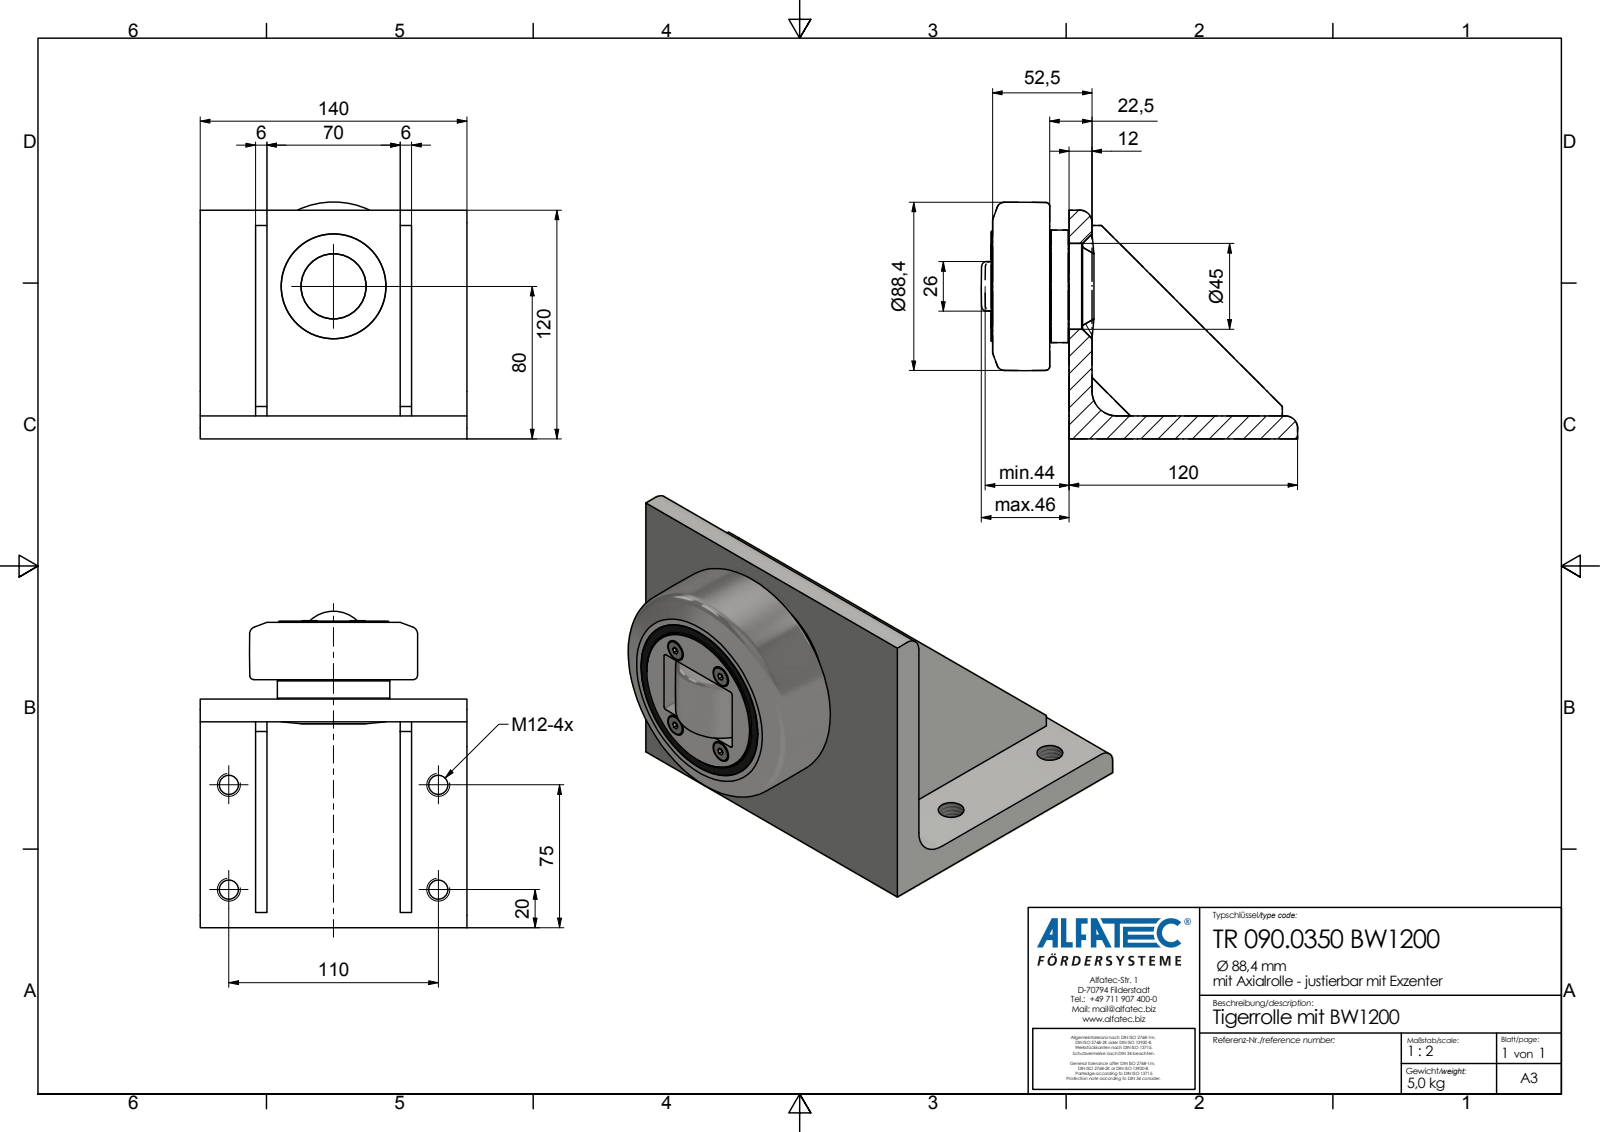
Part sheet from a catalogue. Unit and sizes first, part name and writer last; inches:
Units: inches
Overall size (bounding box): 6.539 × 5.512 × 4.89
Round holes (diameter × count): ⌀0.398 ×4
Round bosses / shafts (diameter × count): ⌀0.307 ×4, ⌀2.323 ×1, ⌀2.276 ×1, ⌀2.177 ×1
Partial cylindrical surfaces — rounded edges, fillets, slot ends (radius × count): R0.039 ×4, R0.256 ×2, R0.512 ×1
Main face-to-face distances: 0.472, 2.992, 0.236, 1.142, 1.378, 4.134, 4.37, 3.228, 2.756, 0.402
Hole centre spacings: 2.165, 4.331, 4.842
Volume: 40.13 in³ · Surface area: 171 in²
Bodies: 1 solid, 97 faces (64 planar, 18 cylindrical, 15 other)
Part name (STEP PRODUCT): TR 090.0350 BW1200_Kontur
STEP written by: Autodesk Inventor 2020 (AP242_MANAGED_MODEL_BASED_3D_ENGINEERING_MIM_LF)
